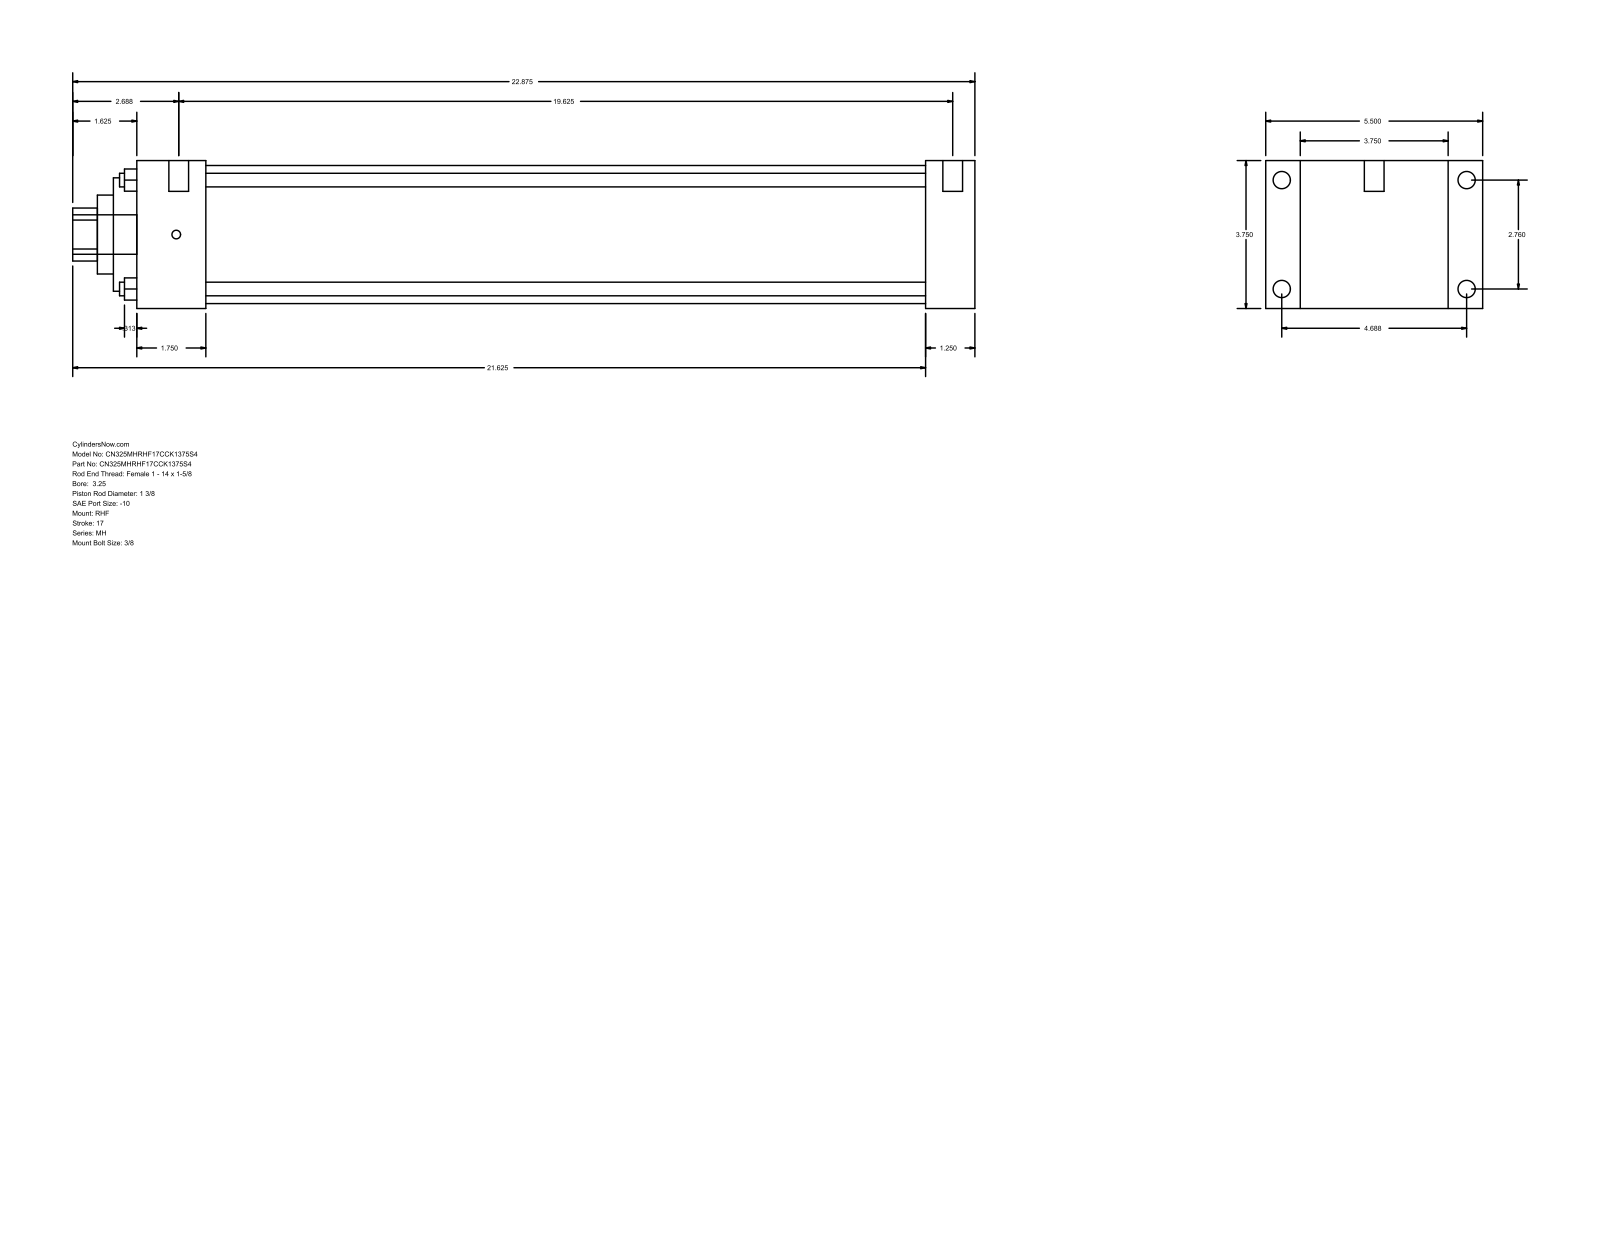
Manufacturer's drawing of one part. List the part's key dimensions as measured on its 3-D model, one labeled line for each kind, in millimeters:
Part name (STEP PRODUCT): MH_RHF__0325_1.375
STEP written by: GSSL Pune (CONFIG_CONTROL_DESIGN)
Units: millimetres
Bodies: 0 solids, 90 faces (61 planar, 29 cylindrical, 0 other)
Overall size (bounding box): 581.02 × 139.7 × 95.25
Round holes (diameter × count): ⌀8.76 ×4, ⌀34.92 ×1, ⌀50.8 ×1, ⌀73.03 ×1, ⌀88.9 ×1
Round bosses / shafts (diameter × count): ⌀11.13 ×4, ⌀5.56 ×4, ⌀12.7 ×2, ⌀25.4 ×1
Partial cylindrical surfaces — rounded edges, fillets, slot ends (radius × count): R17.06 ×1
Main face-to-face distances: 95.24, 31.75, 22.23, 117.47, 508, 539.75, 139.7, 44.45, 463.55, 495.3
Hole centre spacings: 49.57, 70.1, 99.14
